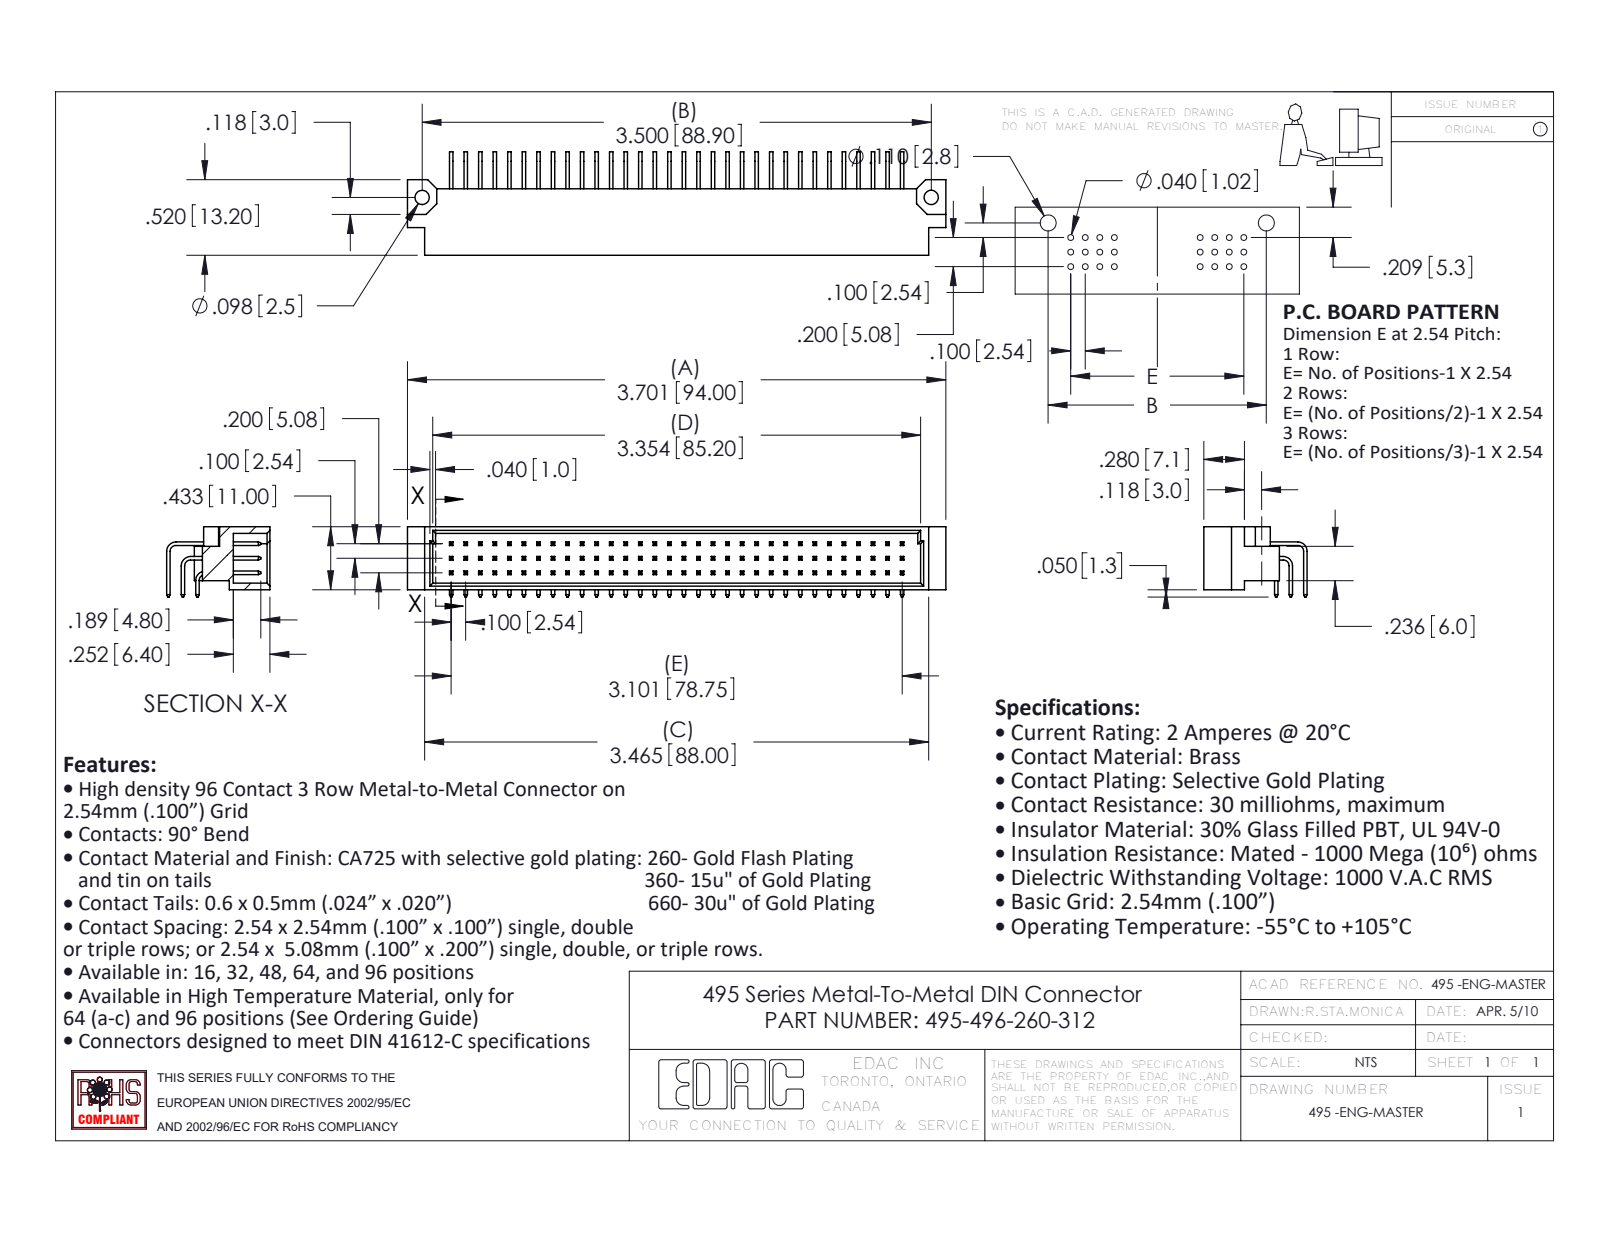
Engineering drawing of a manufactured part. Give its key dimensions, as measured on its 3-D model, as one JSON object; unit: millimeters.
{"part_name": "495-290-3; 495-496-260-312; 495 Part_96; 495-290-1 (+1 more)", "step_written_by": "SolidWorks 2020 (AUTOMOTIVE_DESIGN)", "units": "millimeters", "bodies": {"solids": 97, "faces": 2161, "planar": 1965, "cylindrical": 196, "other": 0}, "overall_size": [94, 18.05, 12.27], "volume_mm3": 6621, "surface_area_mm2": 11442, "round_holes": [[2.49, 2]], "partial_cylinders_radius": [[1.02, 3], [1.65, 3]], "face_to_face_distances": [2.54, 0.61, 5.08, 5.2, 1.14, 9.86, 3.15, 1.93, 11, 8.72], "hole_center_spacings": [88.9]}
